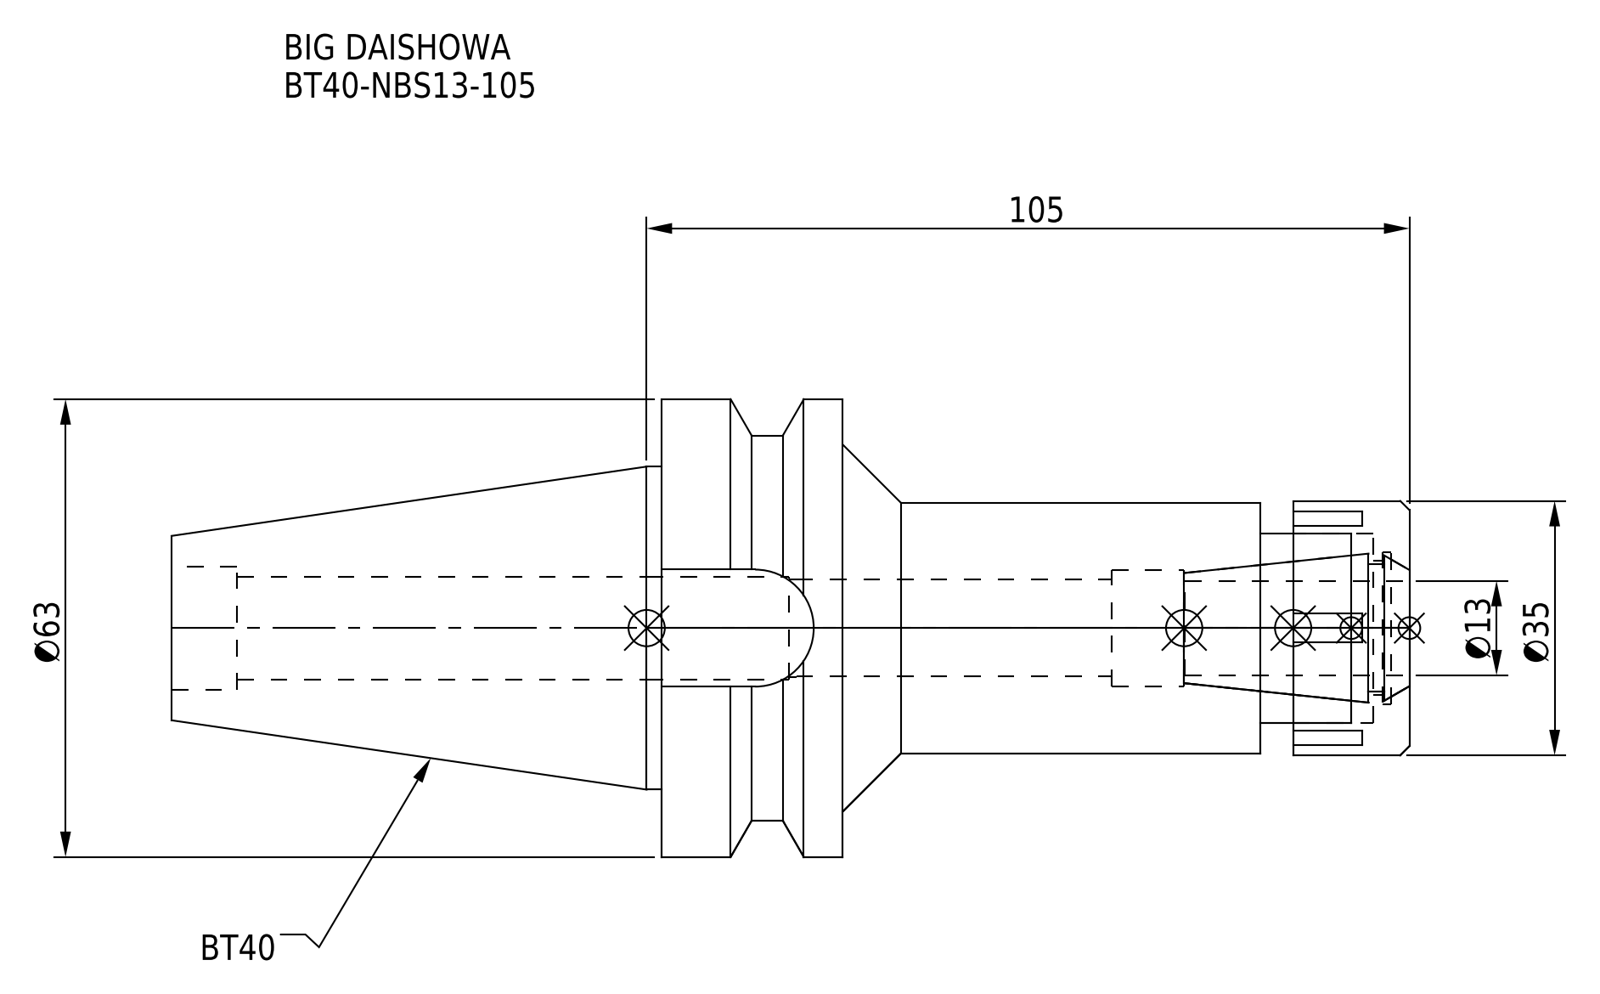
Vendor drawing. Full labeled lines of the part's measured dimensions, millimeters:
Part name (STEP PRODUCT): BT40-NBS13-105.stp; BT40-NBS13-105-FreeParts; BT40-NBS13-105_1.stp; NBN13_1.stp (+3 more)
STEP written by: SolidWorks 2019 (CONFIG_CONTROL_DESIGN)
Units: millimetres
Bodies: 2 solids, 93 faces (45 planar, 34 cylindrical, 14 other)
Overall size (bounding box): 170.4 × 63 × 63
Volume: 178 349 mm³ · Surface area: 37 445 mm²
Round holes (diameter × count): ⌀13.3 ×1, ⌀13.5 ×1, ⌀14.2 ×1, ⌀16 ×1, ⌀17 ×1, ⌀18.5 ×1, ⌀21 ×1, ⌀26 ×1
Round bosses / shafts (diameter × count): ⌀63 ×1, ⌀53 ×1, ⌀44.45 ×1, ⌀35 ×1, ⌀34.5 ×1
Partial cylindrical surfaces — rounded edges, fillets, slot ends (radius × count): R8.05 ×1
Main face-to-face distances: 25, 78, 103, 20.5, 62, 8, 57.5, 82.5, 16, 4.5
